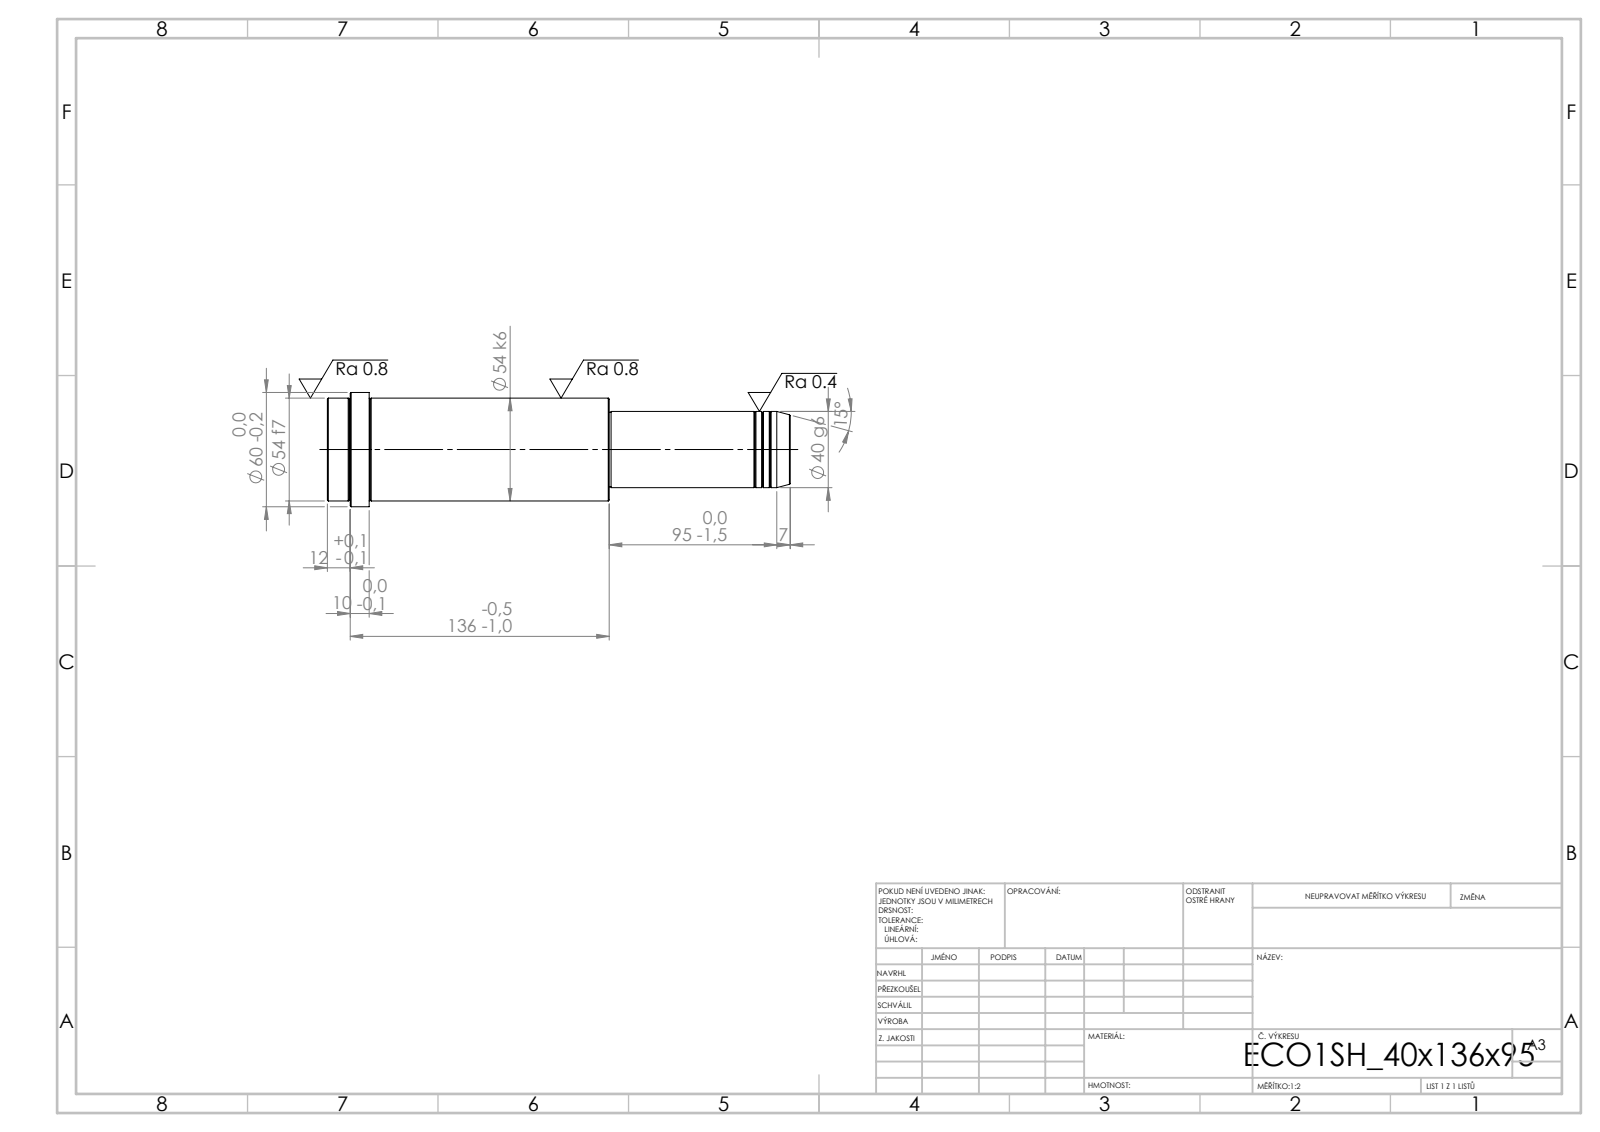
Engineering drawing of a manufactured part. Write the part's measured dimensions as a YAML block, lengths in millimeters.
step_written_by: "SolidWorks 2019 (CONFIG_CONTROL_DESIGN)"
units: millimeters
bodies: {solids: 1, faces: 52, planar: 6, cylindrical: 16, other: 30}
overall_size: [243, 60, 60]
volume: 462497
surface_area: 42998
round_bosses_or_shafts:
  - {diameter: 60, count: 1}
  - {diameter: 54, count: 1}
  - {diameter: 40, count: 1}
  - {diameter: 39, count: 1}
face_to_face_distances: [148, 95, 243, 221, 126, 22, 231, 136, 10, 12]
